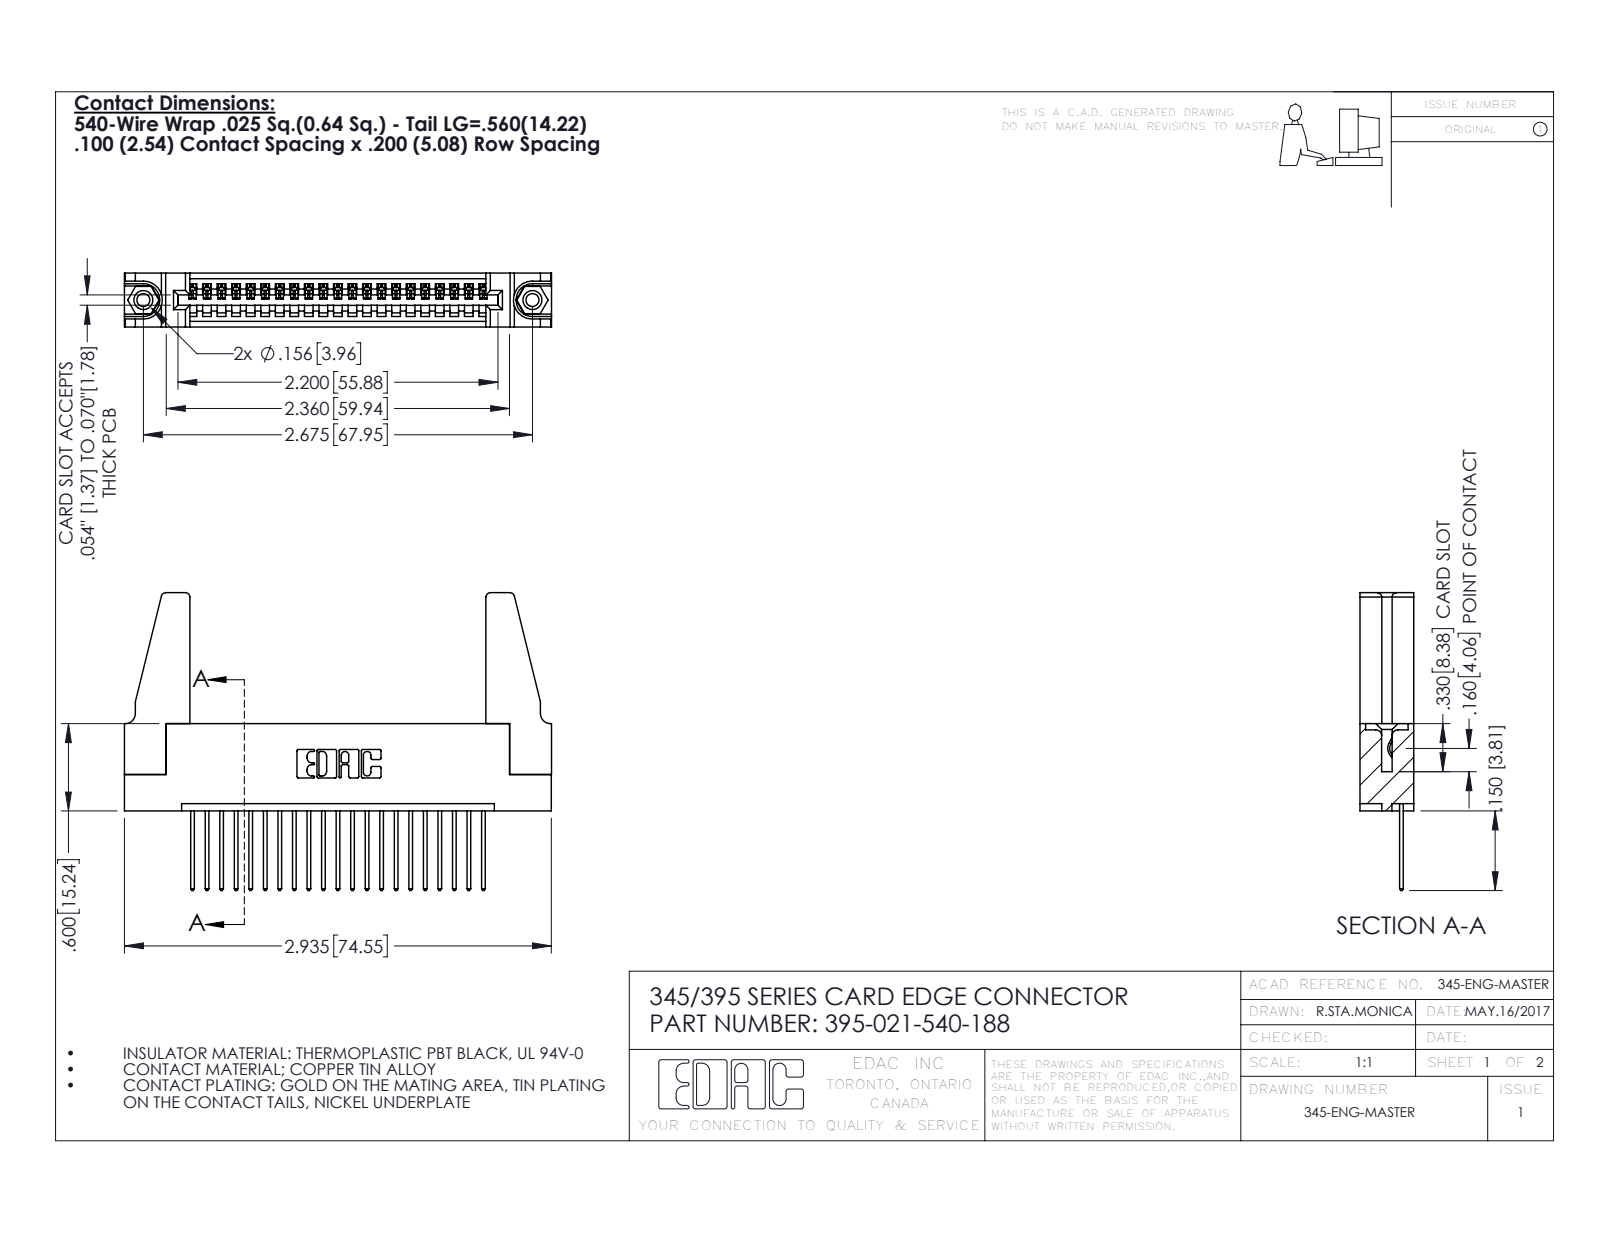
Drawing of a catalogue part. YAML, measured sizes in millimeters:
part_name: "395-021-540-188; 345-220-078_345-220-088; 345-250-001_345-250-001-102; 345-292-001_345-293-140 (+1 more)"
step_written_by: "SolidWorks 2016 (CONFIG_CONTROL_DESIGN)"
units: millimeters
bodies: {solids: 26, faces: 1468, planar: 992, cylindrical: 460, other: 16}
overall_size: [74.6, 52, 9.4]
volume: 10200
surface_area: 12270
round_holes:
  - {diameter: 2.3, count: 2}
  - {diameter: 3.2, count: 2}
  - {diameter: 4, count: 2}
  - {diameter: 1.6, count: 1}
round_bosses_or_shafts:
  - {diameter: 3.9, count: 2}
partial_cylinders:
  - {radius: 0.2, count: 42}
  - {radius: 0.3, count: 42}
  - {radius: 0.3, count: 22}
  - {radius: 0.8, count: 8}
  - {radius: 0.2, count: 6}
  - {radius: 0.8, count: 6}
  - {radius: 0.7, count: 3}
  - {radius: 0.8, count: 2}
face_to_face_distances: [1.8, 9.4, 7.6, 5.1, 2.5, 6.9, 0.6, 5.7, 3.8, 3.8]
hole_center_spacings: [6.9, 62, 67.9]
